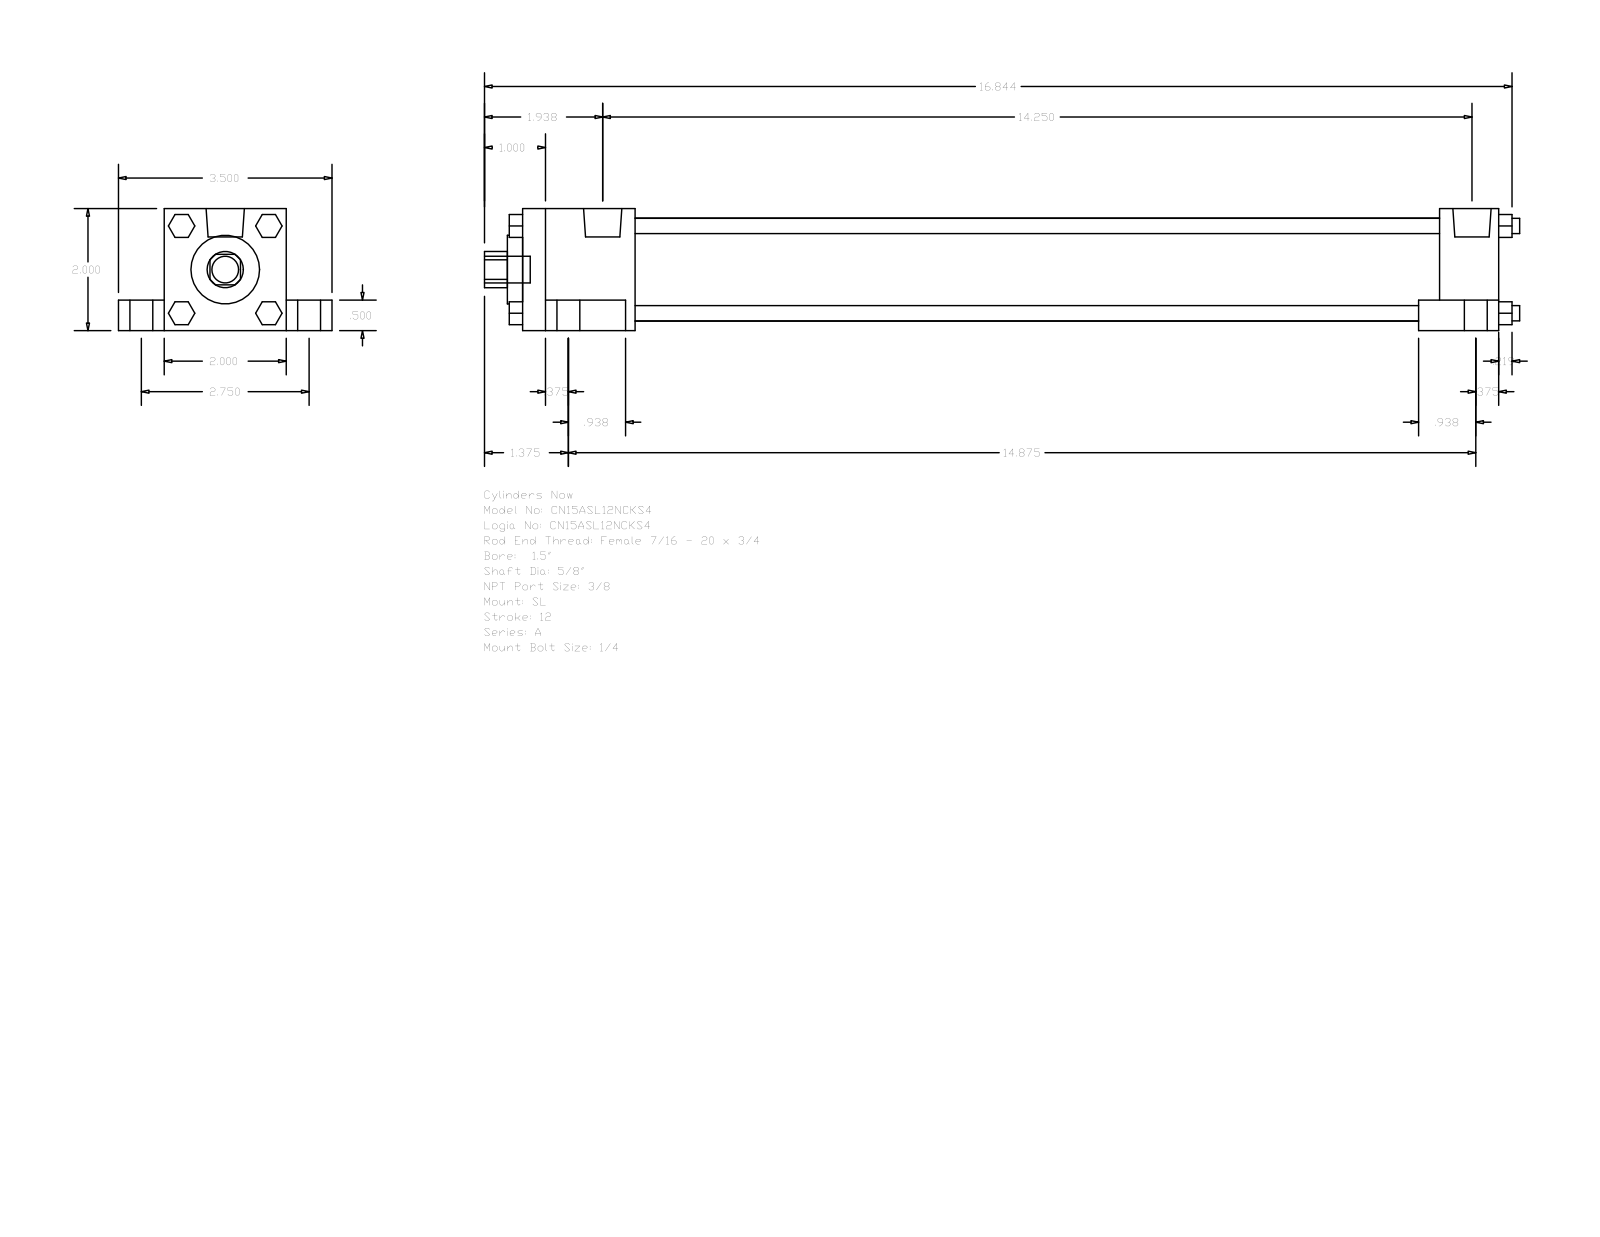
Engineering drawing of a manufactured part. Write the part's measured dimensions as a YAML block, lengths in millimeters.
part_name: "A_SL__0150_0.625"
step_written_by: "GSSL Pune (CONFIG_CONTROL_DESIGN)"
units: millimeters
bodies: {solids: 0, faces: 148, planar: 112, cylindrical: 36, other: 0}
overall_size: [431.01, 88.9, 50.8]
round_holes:
  - {diameter: 15.88, count: 1}
  - {diameter: 28.57, count: 1}
  - {diameter: 42.93, count: 1}
round_bosses_or_shafts:
  - {diameter: 15.88, count: 4}
  - {diameter: 9.53, count: 4}
  - {diameter: 6.35, count: 4}
  - {diameter: 5.56, count: 4}
  - {diameter: 15.93, count: 2}
  - {diameter: 11.11, count: 1}
partial_cylinders:
  - {radius: 7.54, count: 1}
face_to_face_distances: [50.8, 19.05, 12.7, 38.1, 69.85, 406.39, 9.52, 381.79, 24.6, 46.83]
